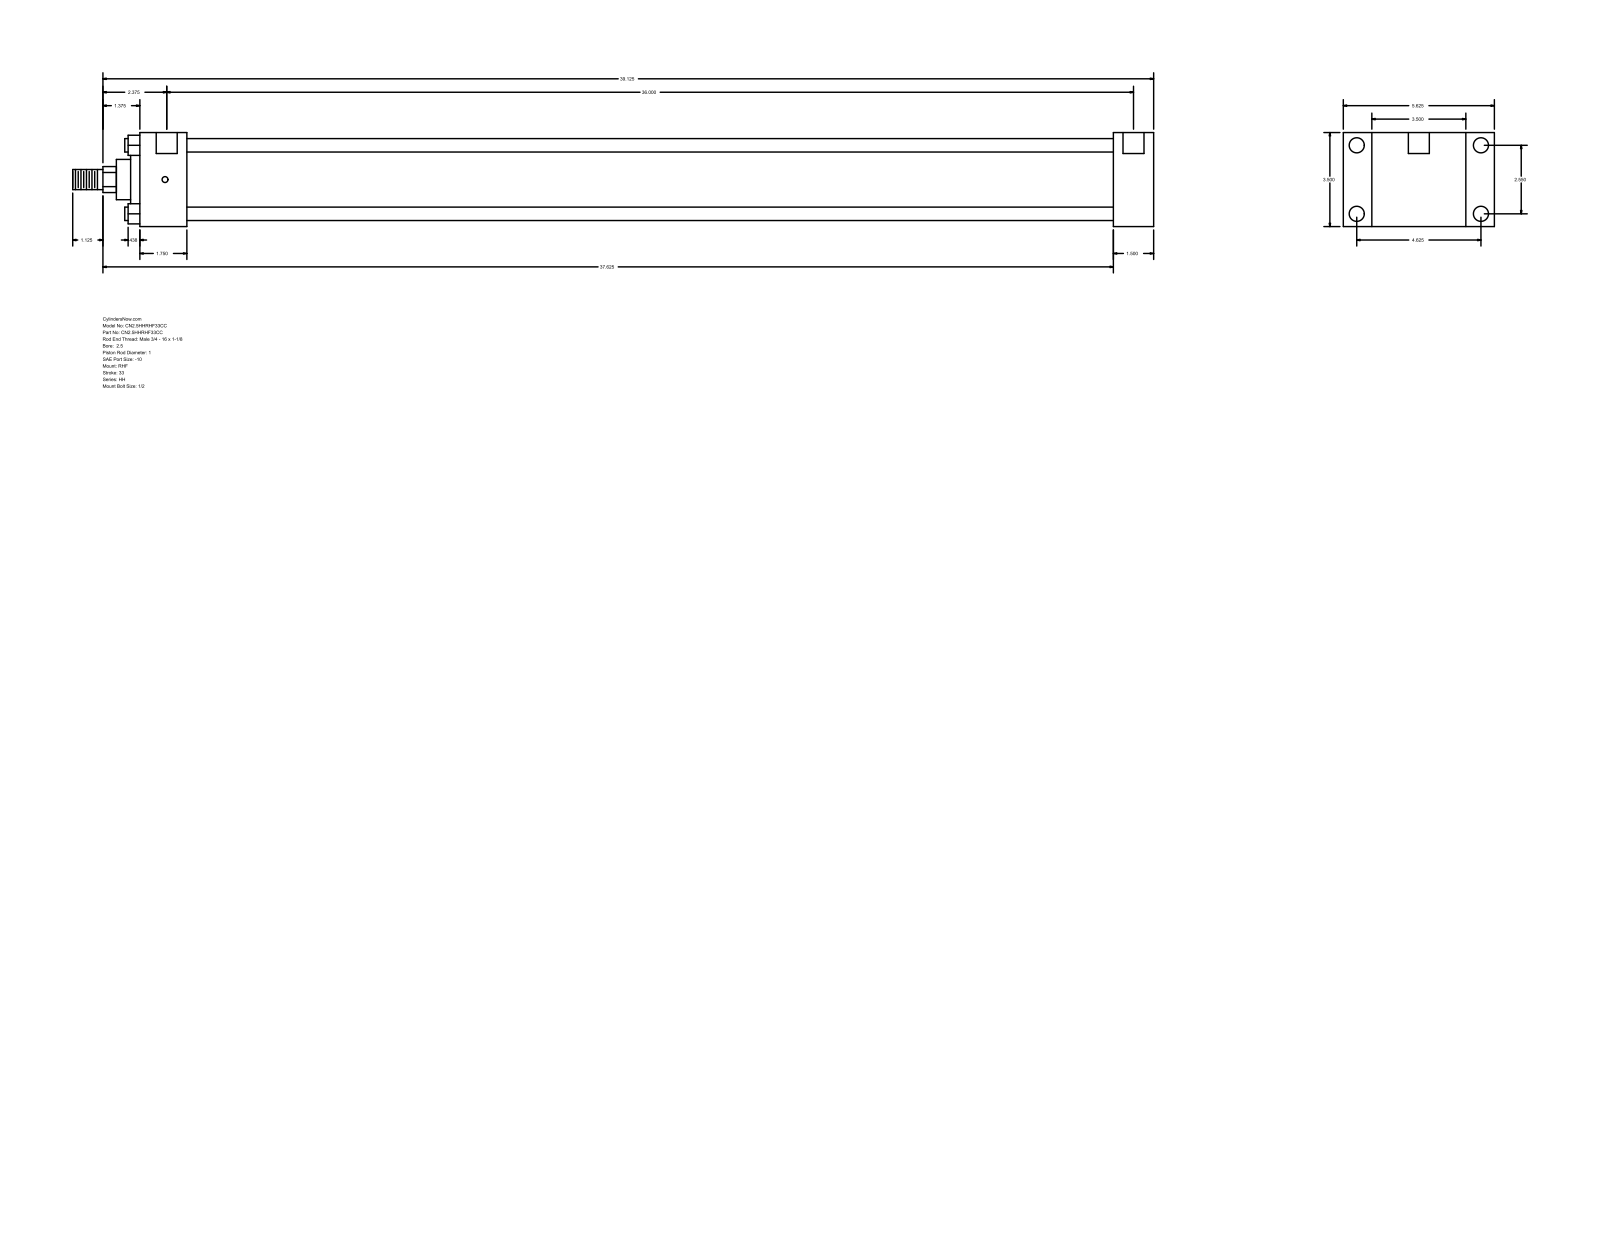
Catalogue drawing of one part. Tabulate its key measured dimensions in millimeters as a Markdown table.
| quantity | value |
| --- | --- |
| part name | HH_RHF__0250_1 |
| STEP written by | GSSL Pune (CONFIG_CONTROL_DESIGN) |
| units | millimeters |
| bodies | 0 solids, 90 faces (61 planar, 29 cylindrical, 0 other) |
| overall size | 1022.35 × 142.88 × 88.9 |
| round holes (diameter × count) | 5.56 × 4, 14.3 × 4, 19.84 × 2 |
| round bosses / shafts (diameter × count) | 12.7 × 4, 73.03 × 1, 60.33 × 1, 38.1 × 1, 25.4 × 1, 19.05 × 1 |
| partial cylindrical surfaces (radius × count) | 12.29 × 1 |
| main face-to-face distances | 88.9, 38.1, 26.99, 115.89, 920.75, 958.85, 142.88, 44.46, 876.29, 914.39 |
| hole center spacings | 64.76, 117.48, 134.15, 917.57, 1.58, 1.59, 914.4, 915.98 |
